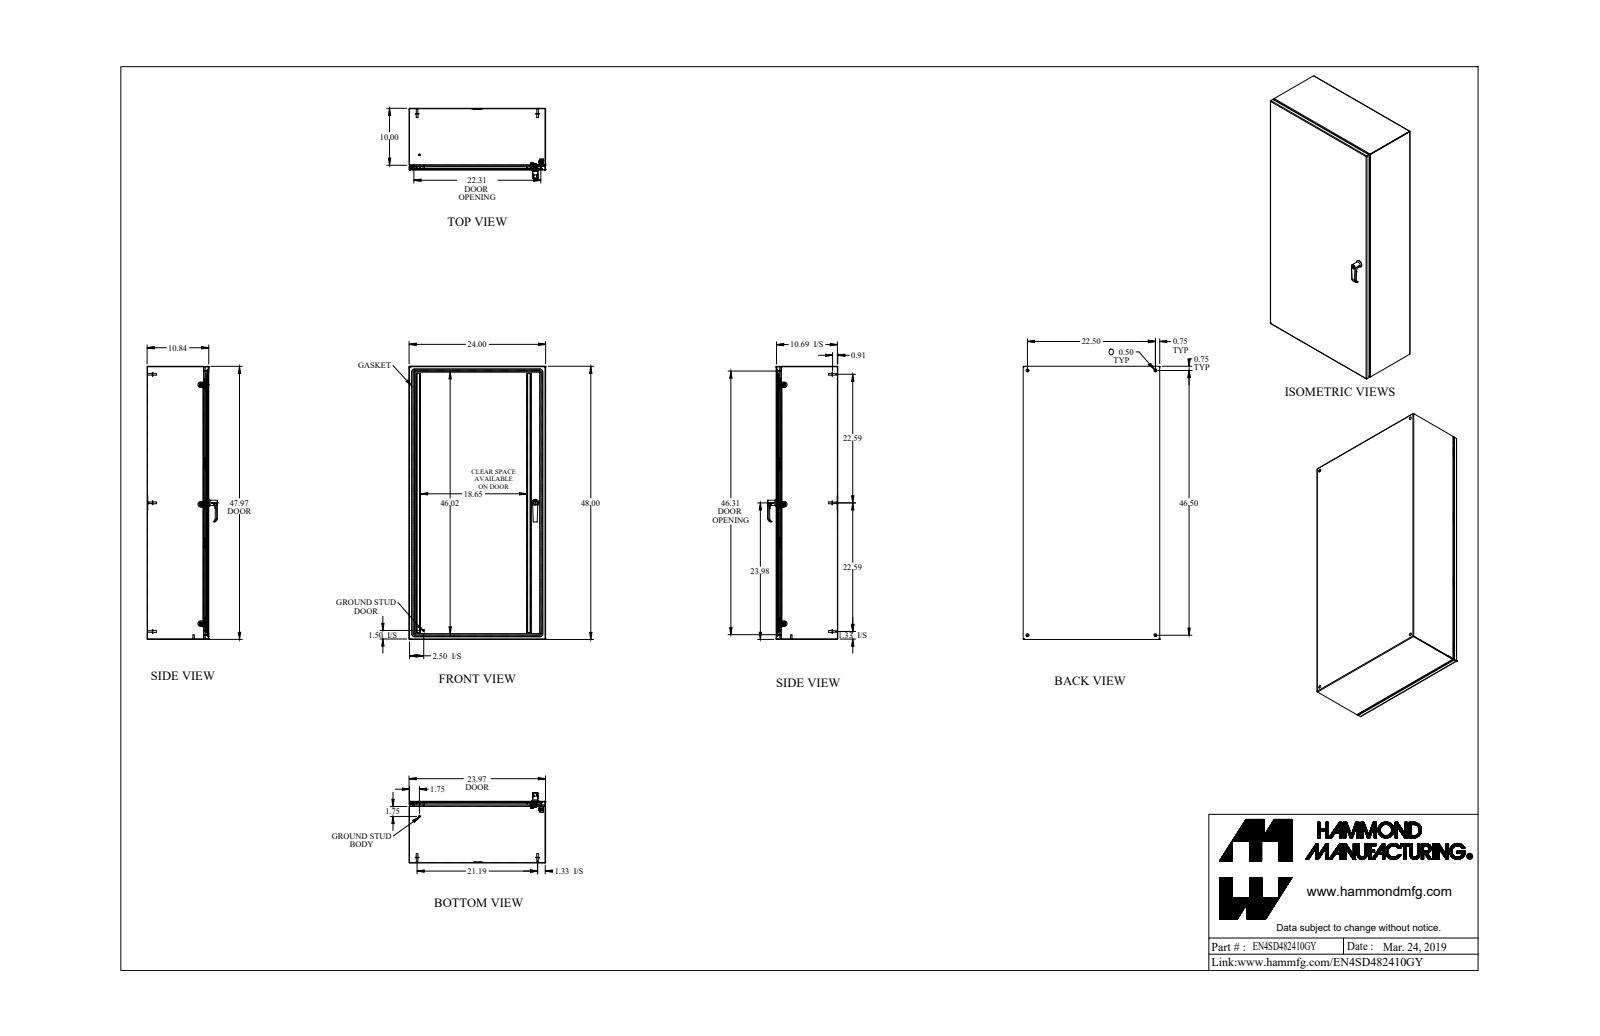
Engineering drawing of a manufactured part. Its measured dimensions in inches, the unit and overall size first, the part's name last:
Units: inches
Overall size (bounding box): 48 × 24 × 12.367
Round holes (diameter × count): ⌀0.176 ×6, ⌀0.5 ×4, ⌀0.196 ×3, ⌀0.25 ×3, ⌀0.265 ×3, ⌀0.413 ×3, ⌀0.256 ×2, ⌀0.313 ×2, ⌀0.394 ×2, ⌀0.172 ×1, ⌀0.24 ×1, ⌀0.242 ×1
Round bosses / shafts (diameter × count): ⌀0.25 ×7, ⌀0.625 ×6, ⌀0.375 ×6, ⌀0.313 ×6, ⌀0.27 ×6, ⌀0.156 ×6, ⌀1 ×3, ⌀0.63 ×2
Partial cylindrical surfaces — rounded edges, fillets, slot ends (radius × count): R0.036 ×20, R0.108 ×20, R0.03 ×15, R0.043 ×12, R0.081 ×12, R0.006 ×8, R0.04 ×8, R0.062 ×8
Main face-to-face distances: 0.072, 10.765, 10.693, 10.837, 23.928, 23.856, 24, 0.072, 47.928, 47.928
Hole centre spacings: 0.787, 20.982, 21, 21.546, 22.5, 41.969, 46.5, 51.657
Volume: 319.5 in³ · Surface area: 8 869 in²
Bodies: 53 solids, 1457 faces (632 planar, 538 cylindrical, 287 other)
Part name (STEP PRODUCT): EN4SD482410GY
STEP written by: SolidWorks 2018 (AUTOMOTIVE_DESIGN)
